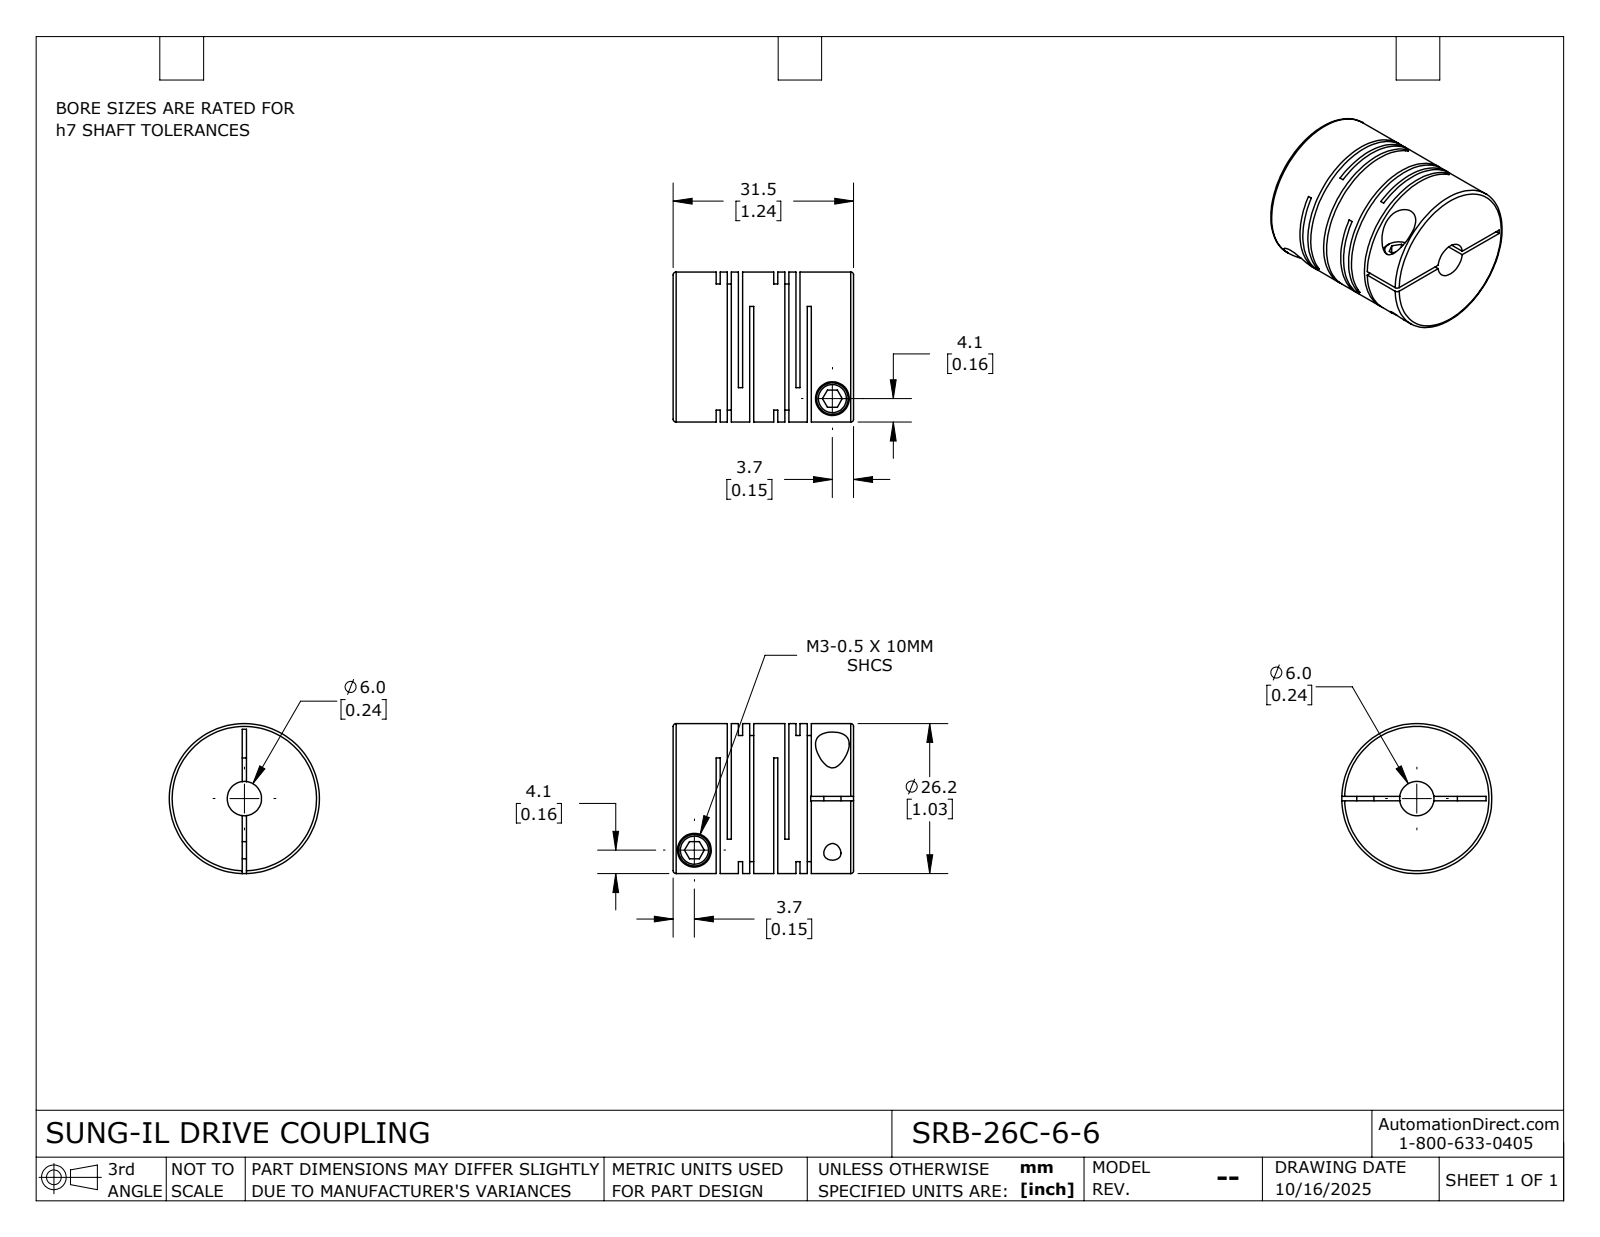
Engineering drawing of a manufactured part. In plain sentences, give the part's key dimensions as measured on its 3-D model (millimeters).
The part is named "SRB-26C-6-6". Its 3-D file was written by "SolidWorks 2024 (CONFIG_CONTROL_DESIGN)". It is 1 solid with 115 faces: 60 planar, 42 cylindrical and 13 other. Overall it measures 31.5 by 26.2 by 26.2 millimeters. Its volume is 13 195 cubic millimeters and its surface area 11 411 square millimeters. Round holes: 2 of diameter 3, 2 of diameter 5.9, 1 of diameter 6. Round bosses or shafts: 2 of diameter 5.5, 1 of diameter 26.2. The main face-to-face distances are 1.95, 10.05, 0.71, 3.9, 8.1, 12, 1.24, 2.66, 9.34, 13.95.
